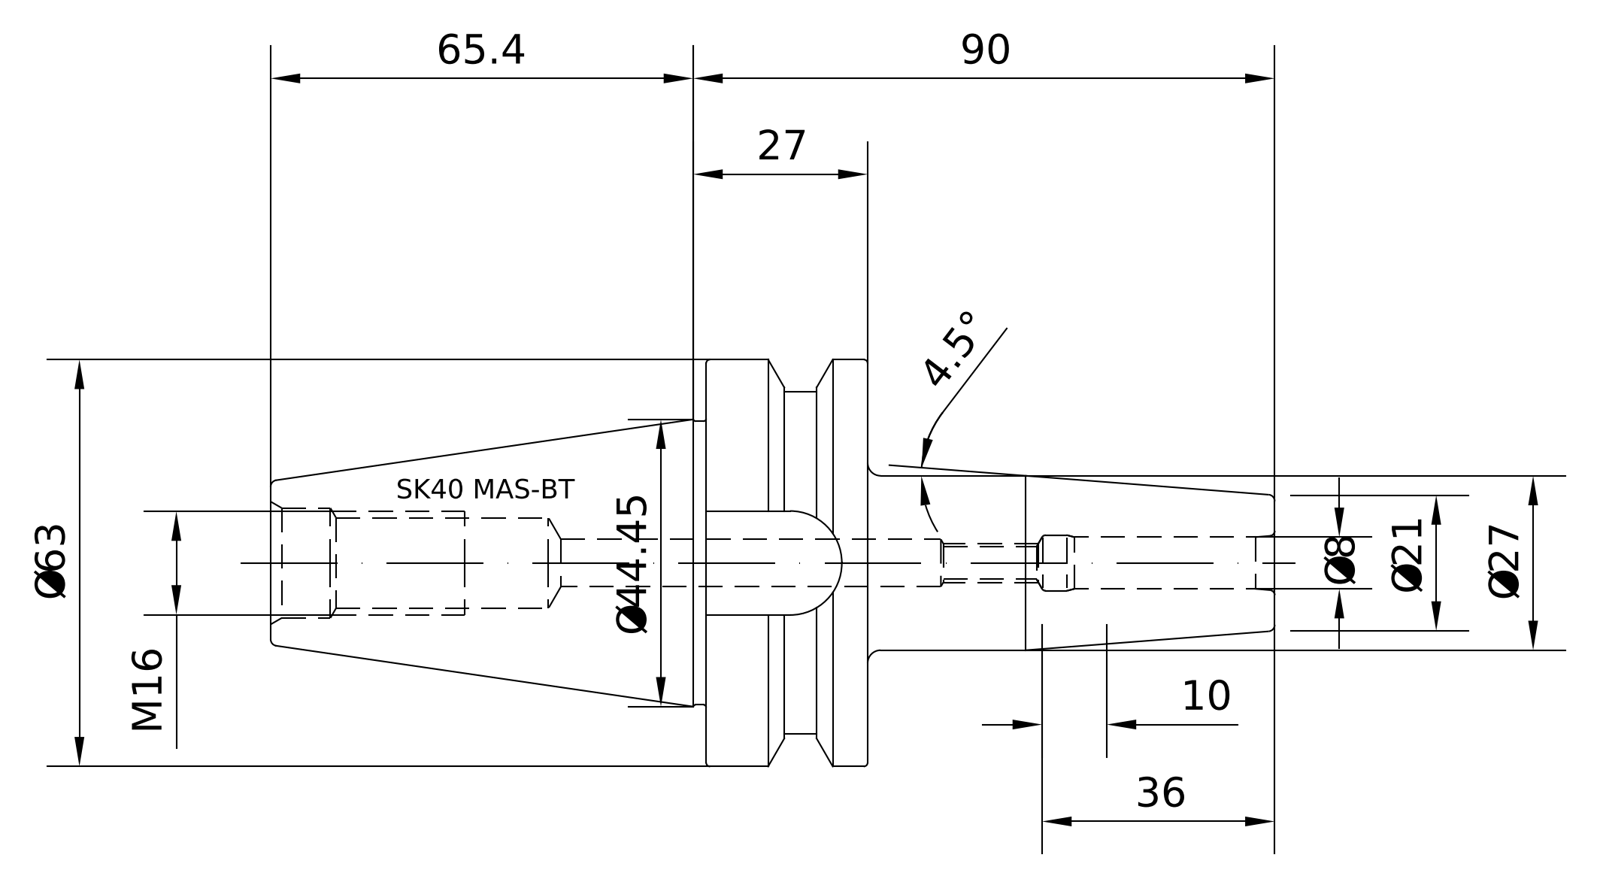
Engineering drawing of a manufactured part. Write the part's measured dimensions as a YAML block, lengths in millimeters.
part_name: "40-640-08"
step_written_by: "PRO/ENGINEER BY PARAMETRIC TECHNOLOGY CORPORATION, 2010430 (CONFIG_CONTROL_DESIGN)"
units: millimeters
bodies: {solids: 1, faces: 96, planar: 26, cylindrical: 22, other: 48}
overall_size: [155.4, 62.98, 62.98]
volume: 155976
surface_area: 27411
round_holes:
  - {diameter: 8, count: 1}
  - {diameter: 13.84, count: 1}
  - {diameter: 17.01, count: 1}
  - {diameter: 17.5, count: 1}
round_bosses_or_shafts:
  - {diameter: 62.98, count: 1}
  - {diameter: 52.75, count: 1}
  - {diameter: 43.75, count: 1}
  - {diameter: 27, count: 1}
  - {diameter: 16.01, count: 1}
partial_cylinders:
  - {radius: 8.1, count: 1}
face_to_face_distances: [25, 44.9, 88, 63, 16.2, 67.4, 92.4, 155.4, 36, 119.4]
